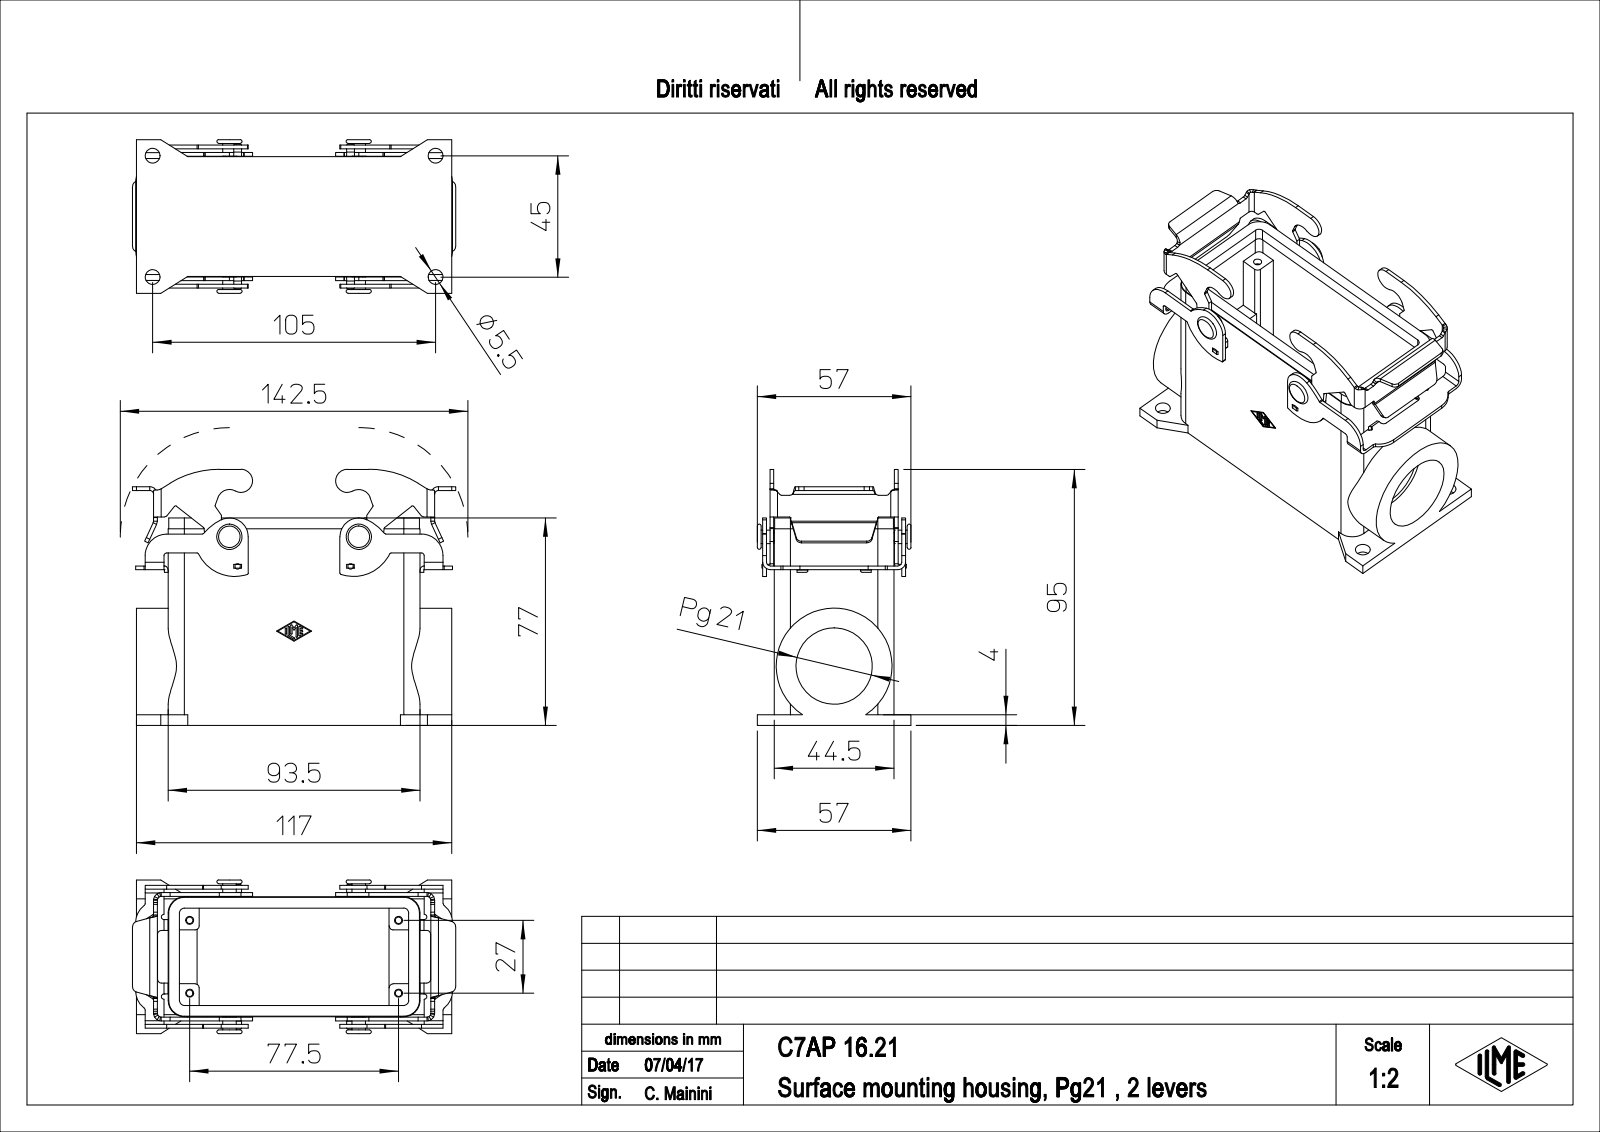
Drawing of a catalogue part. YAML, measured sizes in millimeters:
part_name: "C7AP_16.21"
step_written_by: "PTC Creo Elements/Direct Modeling 19.0E 27-Jun-2016 (C) Parametric Technology GmbH (AUTOMOTIVE_DESIGN)"
units: millimeters
bodies: {solids: 1, faces: 596, planar: 290, cylindrical: 266, other: 40}
overall_size: [119.97, 95, 57]
volume: 143298
surface_area: 70489
round_holes:
  - {diameter: 2.46, count: 4}
  - {diameter: 3, count: 4}
  - {diameter: 5.5, count: 4}
  - {diameter: 24.5, count: 1}
  - {diameter: 28.3, count: 1}
round_bosses_or_shafts:
  - {diameter: 5, count: 2}
  - {diameter: 3.2, count: 2}
  - {diameter: 3, count: 2}
  - {diameter: 43, count: 1}
partial_cylinders:
  - {radius: 0.5, count: 22}
  - {radius: 1, count: 20}
  - {radius: 0.25, count: 16}
  - {radius: 1.5, count: 14}
  - {radius: 2, count: 12}
  - {radius: 1.4, count: 10}
  - {radius: 2.8, count: 10}
  - {radius: 8, count: 6}
face_to_face_distances: [4, 40.5, 1.4, 44.5, 36.5, 2.7, 48.9, 8.25, 1.55, 5.55]
hole_center_spacings: [16.43, 38.54, 91.69, 98.09, 27, 45, 77.5, 82.07]
